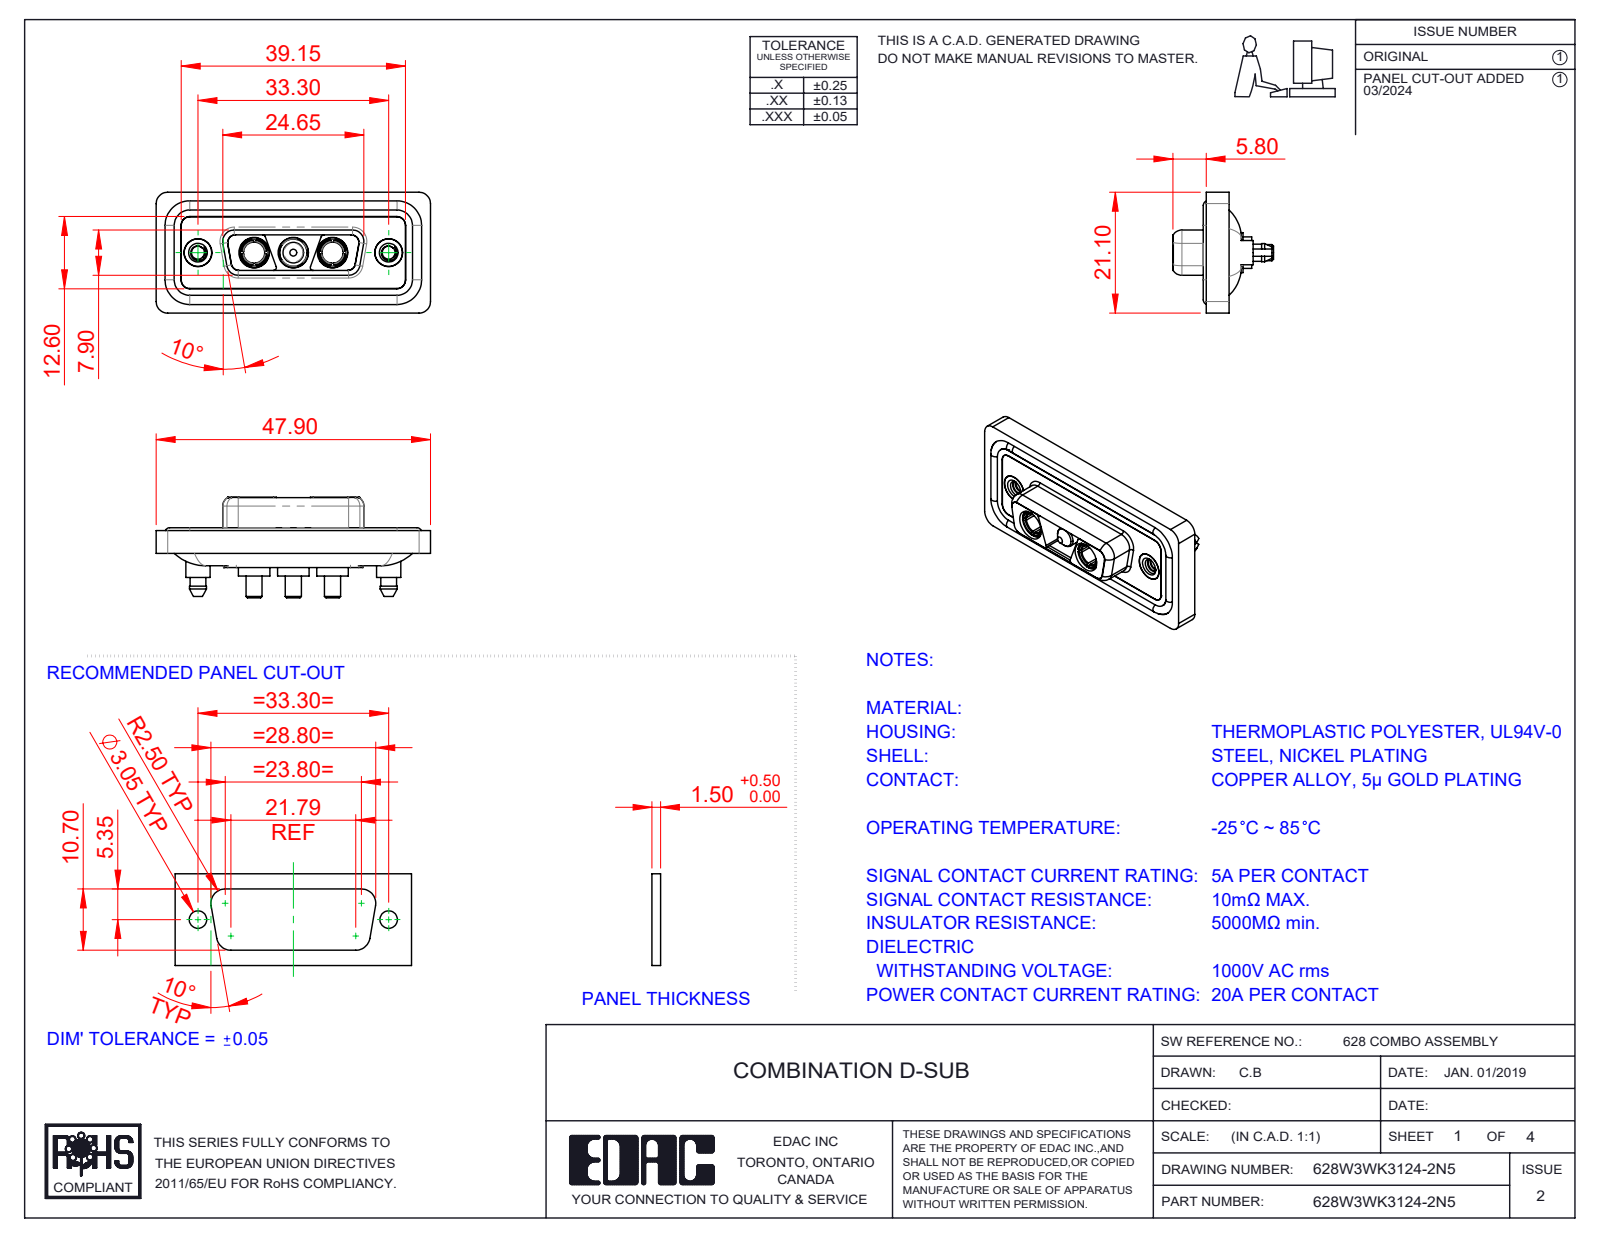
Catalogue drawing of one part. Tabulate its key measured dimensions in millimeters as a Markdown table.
| quantity | value |
| --- | --- |
| part name | 628Combo Shell Rear_15 Contacts; 628Combo Housing_3WK3; 628Combo Waterproof Housing_15 Contacts; 628Combo Threaded Boardlock_5 (+4 more) |
| STEP written by | SolidWorks 2023 (CONFIG_CONTROL_DESIGN) |
| units | millimeters |
| bodies | 13 solids, 633 faces (194 planar, 290 cylindrical, 149 other) |
| overall size | 47.9 × 21.1 × 17.55 |
| volume | 6 012 mm³ |
| surface area | 9 838 mm² |
| round holes (diameter × count) | 4.85 × 5, 5.3 × 3, 2.26 × 2, 3.7 × 2, 4 × 2, 4.05 × 2, 5 × 2 |
| round bosses / shafts (diameter × count) | 1.6 × 4, 5.5 × 3, 5.2 × 3, 4.75 × 3, 3.75 × 3, 2.8 × 3, 5.4 × 2, 4.96 × 2 |
| partial cylindrical surfaces (radius × count) | 1.5 × 24, 2 × 20, 1.35 × 12, 1.6 × 10, 0.5 × 8, 0.25 × 4, 0.6 × 4, 0.65 × 4 |
| main face-to-face distances | 0.4, 1.6, 1.8, 0.5, 1.1, 2.9, 5.65, 7.05, 1.5, 5.35 |
| hole center spacings | 6.85, 9.8, 16.65, 23.5, 13.7, 33.3 |
